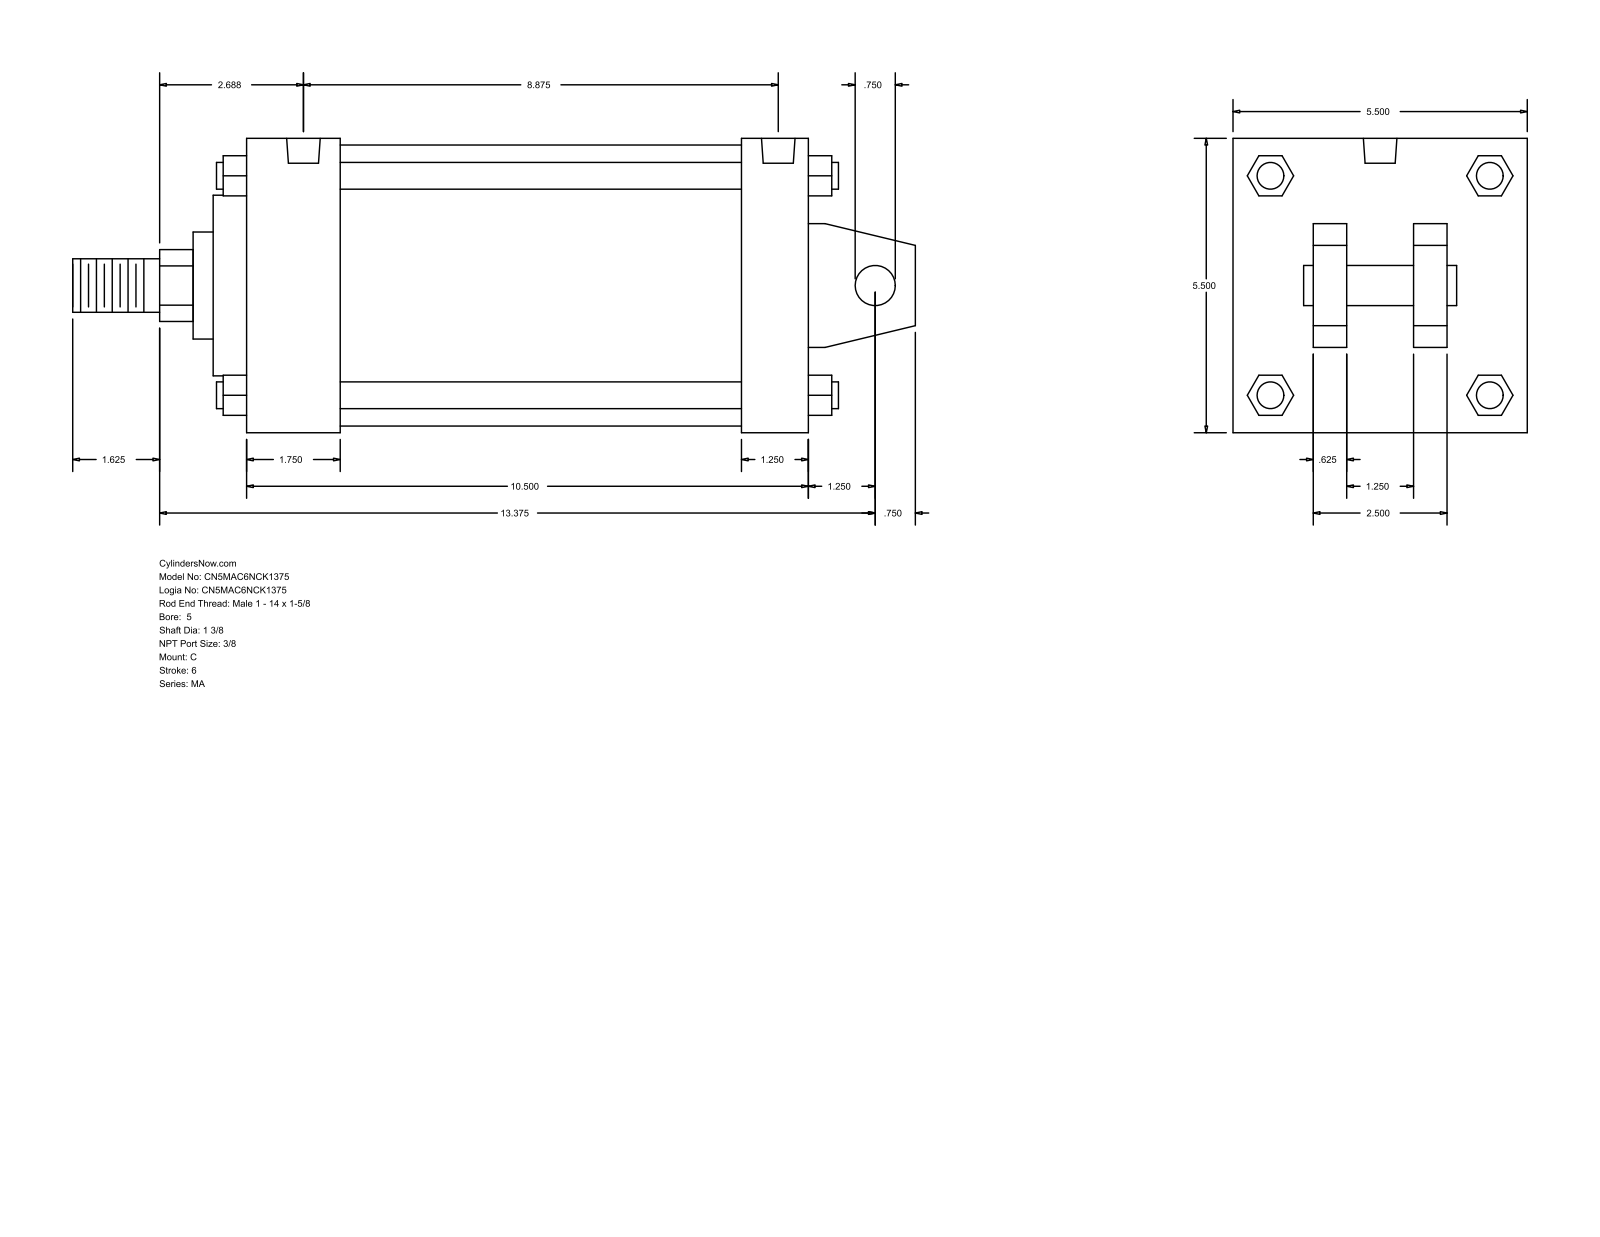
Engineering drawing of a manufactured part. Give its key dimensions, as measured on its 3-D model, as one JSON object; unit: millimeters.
{"part_name": "MA_C__0500_1.375", "step_written_by": "GSSL Pune (CONFIG_CONTROL_DESIGN)", "units": "millimeters", "bodies": {"solids": 0, "faces": 141, "planar": 109, "cylindrical": 32, "other": 0}, "overall_size": [400.05, 139.7, 139.7], "round_holes": [[11.11, 4], [15.93, 2]], "round_bosses_or_shafts": [[12.7, 4], [133.35, 1], [85.72, 1], [50.8, 1], [34.92, 1], [25.4, 1], [19.05, 1]], "partial_cylinders_radius": [[17.06, 1]], "face_to_face_distances": [139.7, 266.71, 15.87, 234.96, 31.75, 44.45, 190.51, 222.26, 53.97, 38.1], "hole_center_spacings": [215.9, 4.76, 4.77, 220.66, 220.67, 225.43]}
